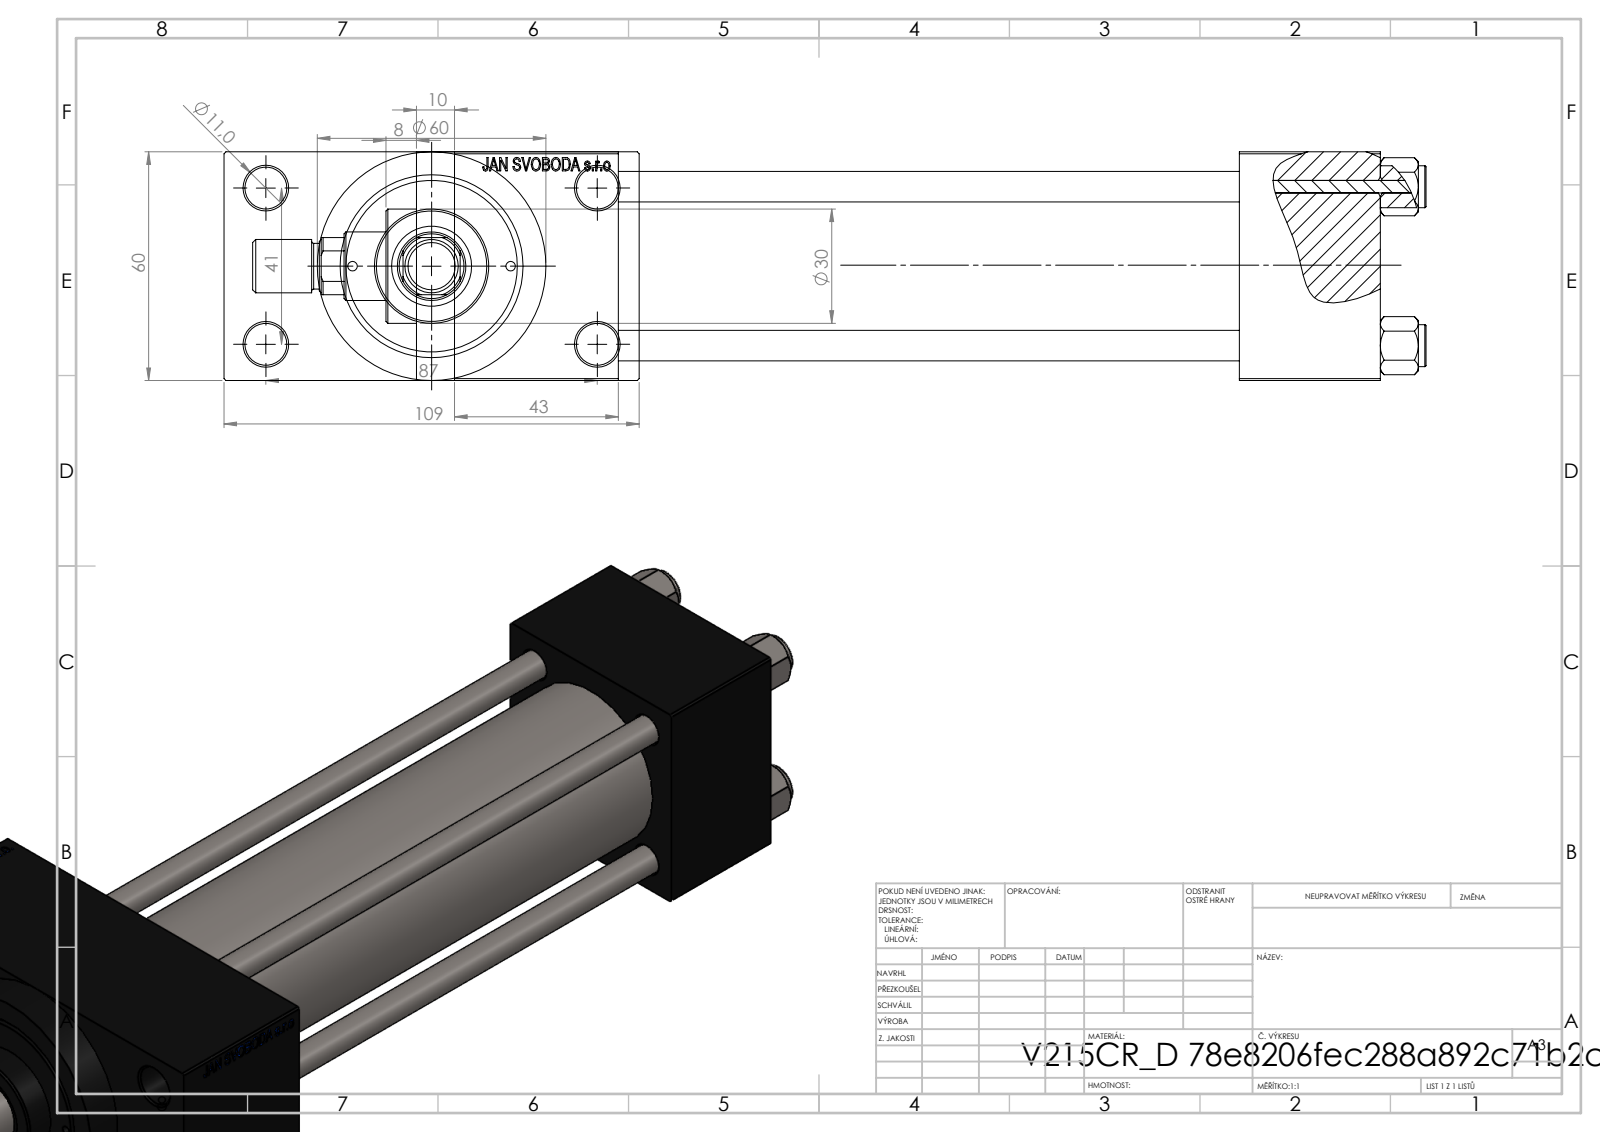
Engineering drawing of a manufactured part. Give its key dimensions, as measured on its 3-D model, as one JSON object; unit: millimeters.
{"part_name": "V215_VC_A; V215CR_VCP_D; ROD_END_AH; V215CR_D_Body (+2 more)", "step_written_by": "SolidWorks 2019 (CONFIG_CONTROL_DESIGN)", "units": "millimeters", "bodies": {"solids": 12, "faces": 1126, "planar": 504, "cylindrical": 96, "other": 526}, "overall_size": [308, 109, 60], "volume_mm3": 605366, "surface_area_mm2": 168492, "round_holes": [[8, 4], [11, 4], [2.5, 2], [7, 2], [16.66, 2], [24, 2], [8.5, 1], [18, 1], [21, 1], [31, 1], [40, 1], [45, 1]], "round_bosses_or_shafts": [[11, 4], [60, 1], [46, 1], [30, 1], [14, 1], [12, 1]], "partial_cylinders_radius": [[8.5, 1]], "face_to_face_distances": [60, 163, 24.5, 84.5, 37, 200, 43, 243, 206, 209.74], "hole_center_spacings": [20.85, 22.65, 29.49, 30.62, 41.7, 46.53, 47.15, 48.09]}
